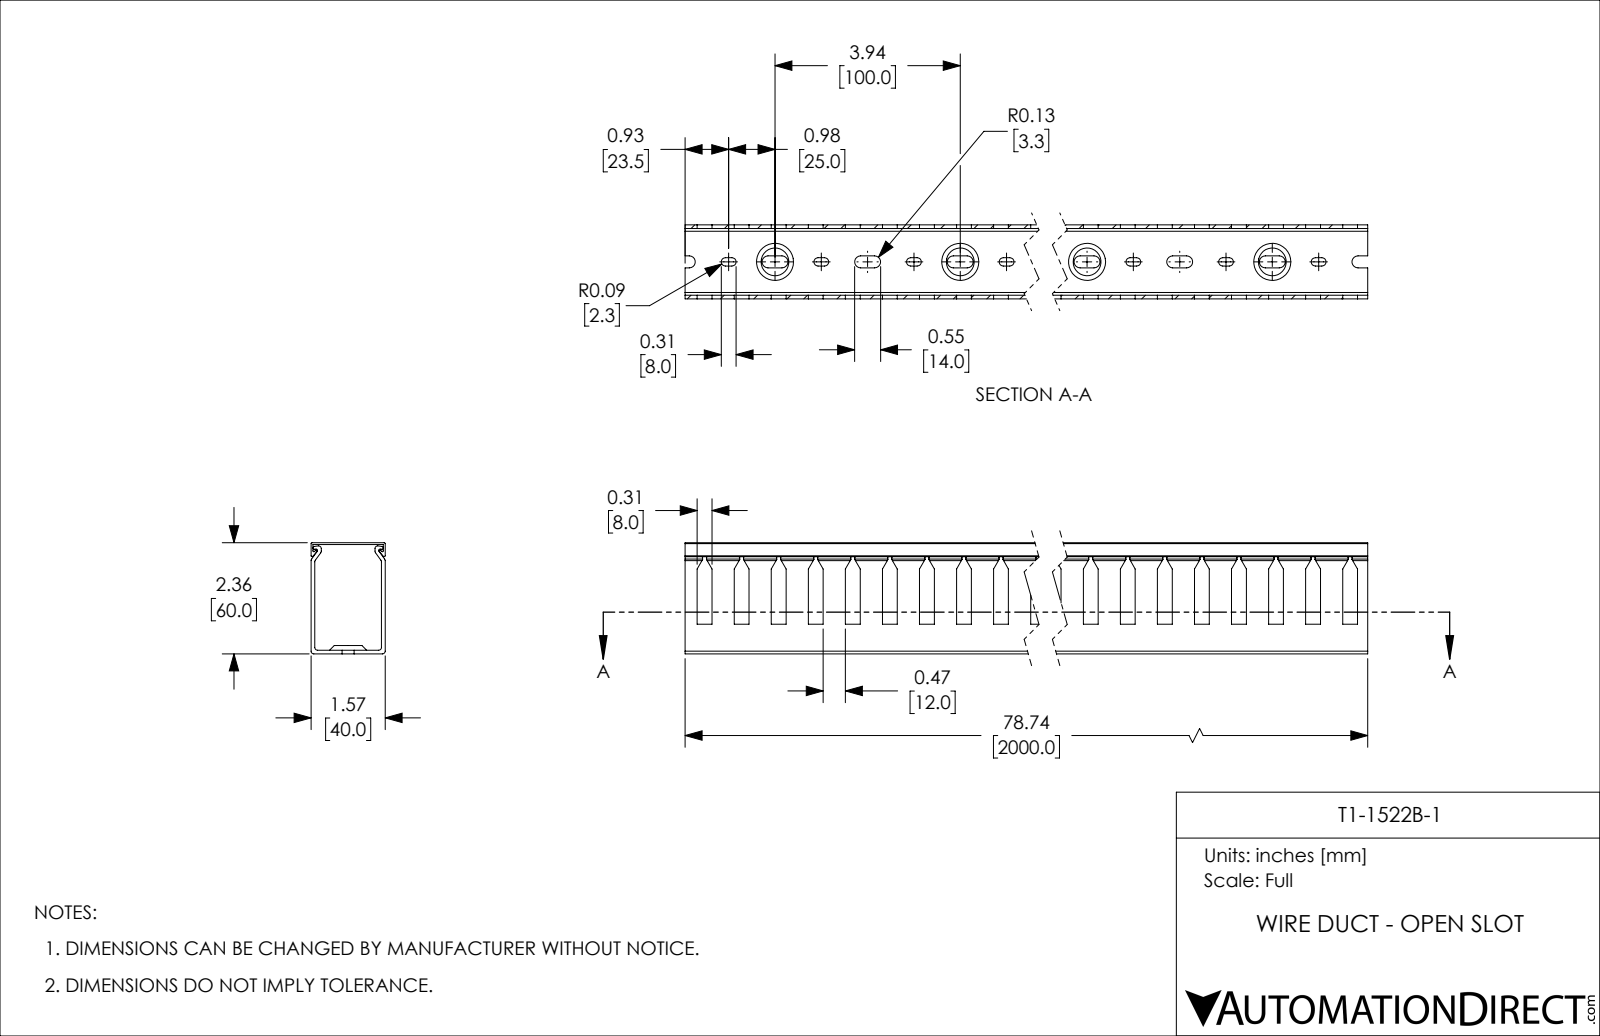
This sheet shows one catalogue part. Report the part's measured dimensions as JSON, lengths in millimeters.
{"part_name": "T1-1522B-1", "step_written_by": "SolidWorks 2021 (CONFIG_CONTROL_DESIGN)", "units": "millimeters", "bodies": {"solids": 2, "faces": 1005, "planar": 534, "cylindrical": 431, "other": 40}, "overall_size": [2000, 60, 40], "volume_mm3": 736952, "surface_area_mm2": 853222, "partial_cylinders_radius": [[2.25, 80], [3.25, 80], [1.5, 12], [0.5, 8], [0.75, 6]], "face_to_face_distances": [2, 38, 40, 1, 36, 60, 59, 57, 58, 39]}
